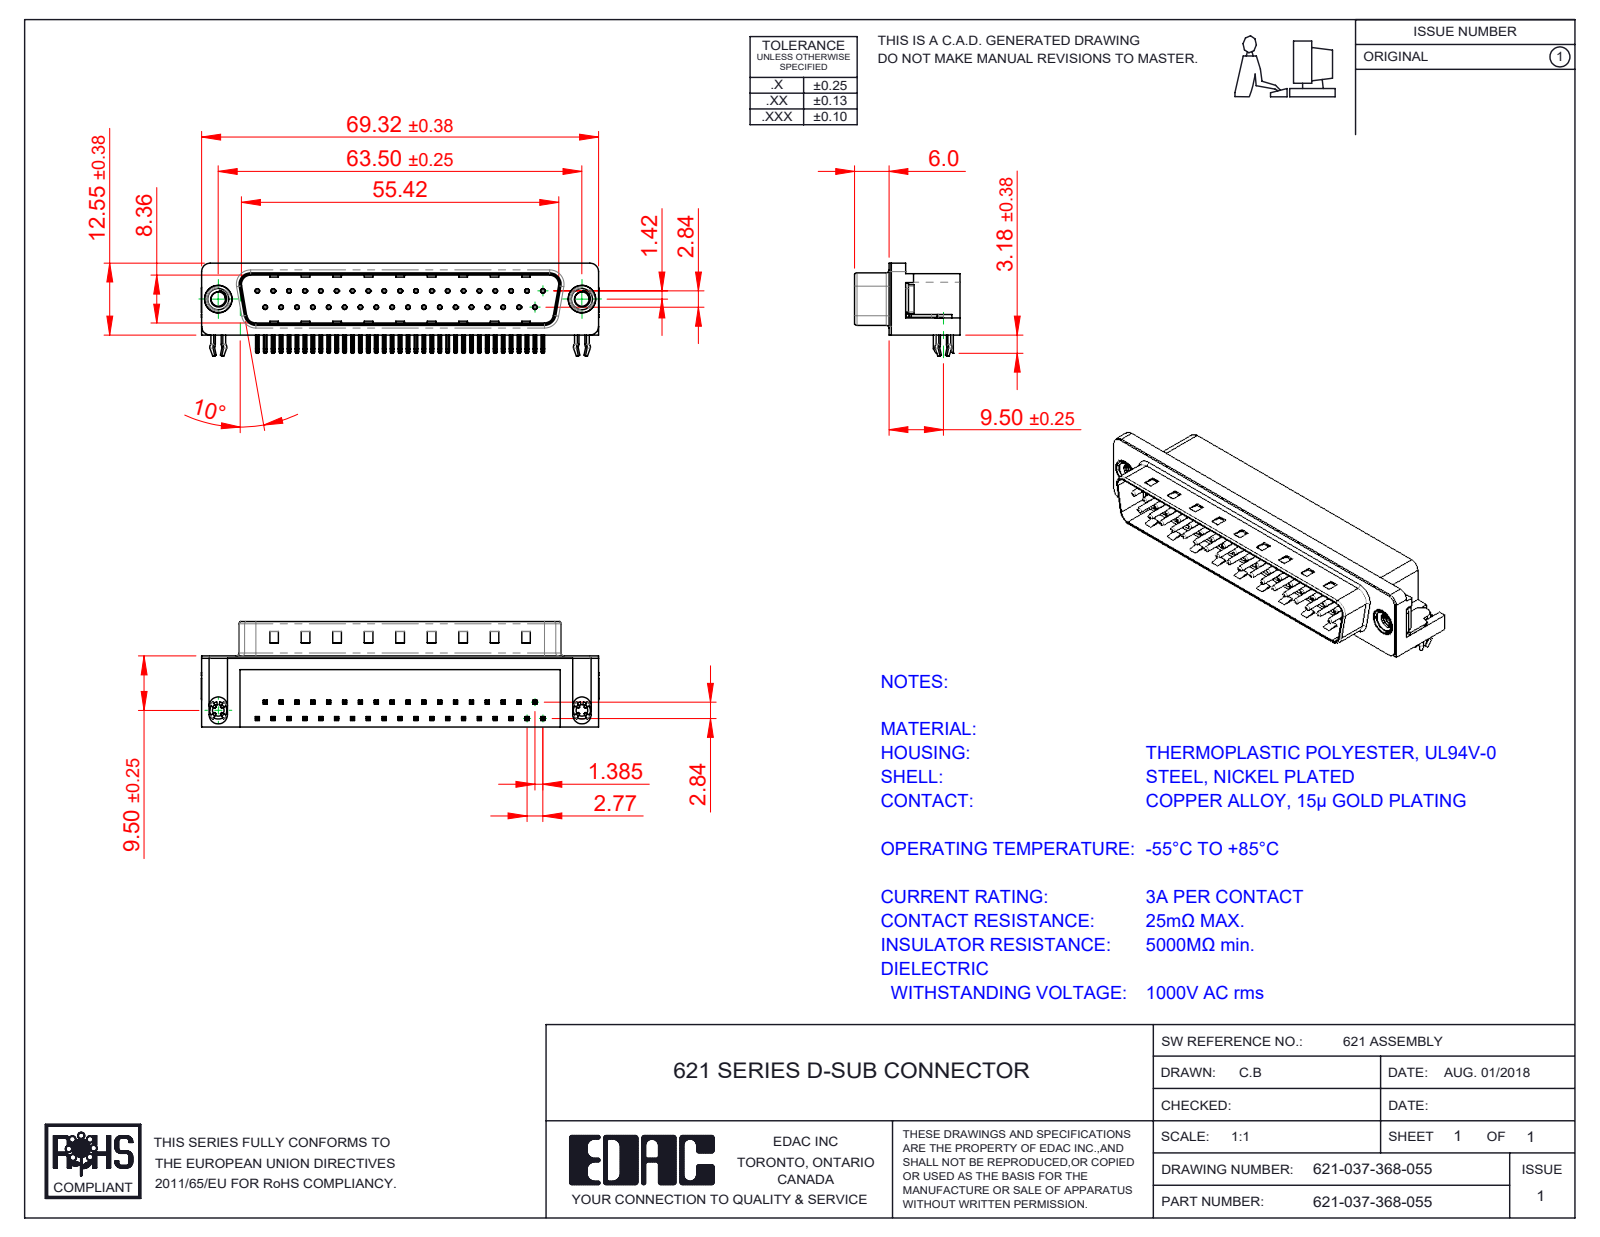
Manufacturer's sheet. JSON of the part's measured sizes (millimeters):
{"part_name": "621 M3 Threaded Rivet; 621 Housing_37 Socket; 621 Contact Top; 621-037-368-055 (+3 more)", "step_written_by": "SolidWorks 2016 (CONFIG_CONTROL_DESIGN)", "units": "millimeters", "bodies": {"solids": 43, "faces": 3229, "planar": 2013, "cylindrical": 931, "other": 285}, "overall_size": [69.4, 18.4, 15.73], "volume_mm3": 8627, "surface_area_mm2": 10177, "round_holes": [[0.35, 37], [0.8, 37], [2.26, 2], [2.5, 2], [4, 2], [4.8, 2], [5, 2]], "round_bosses_or_shafts": [[0.75, 37], [4.9, 2], [4.75, 2], [3.9, 2], [3.26, 2]], "partial_cylinders_radius": [[0.25, 156], [0.12, 74], [1, 16], [0.5, 9], [1.6, 8], [1.5, 7], [0.9, 4], [2, 4]], "face_to_face_distances": [0.4, 12, 10.35, 8.76, 2.1, 1.7, 10.46, 10.86, 9, 12.4], "hole_center_spacings": [3.16, 2.77, 5.54, 8.31, 11.08, 13.85, 19.39, 22.16]}
